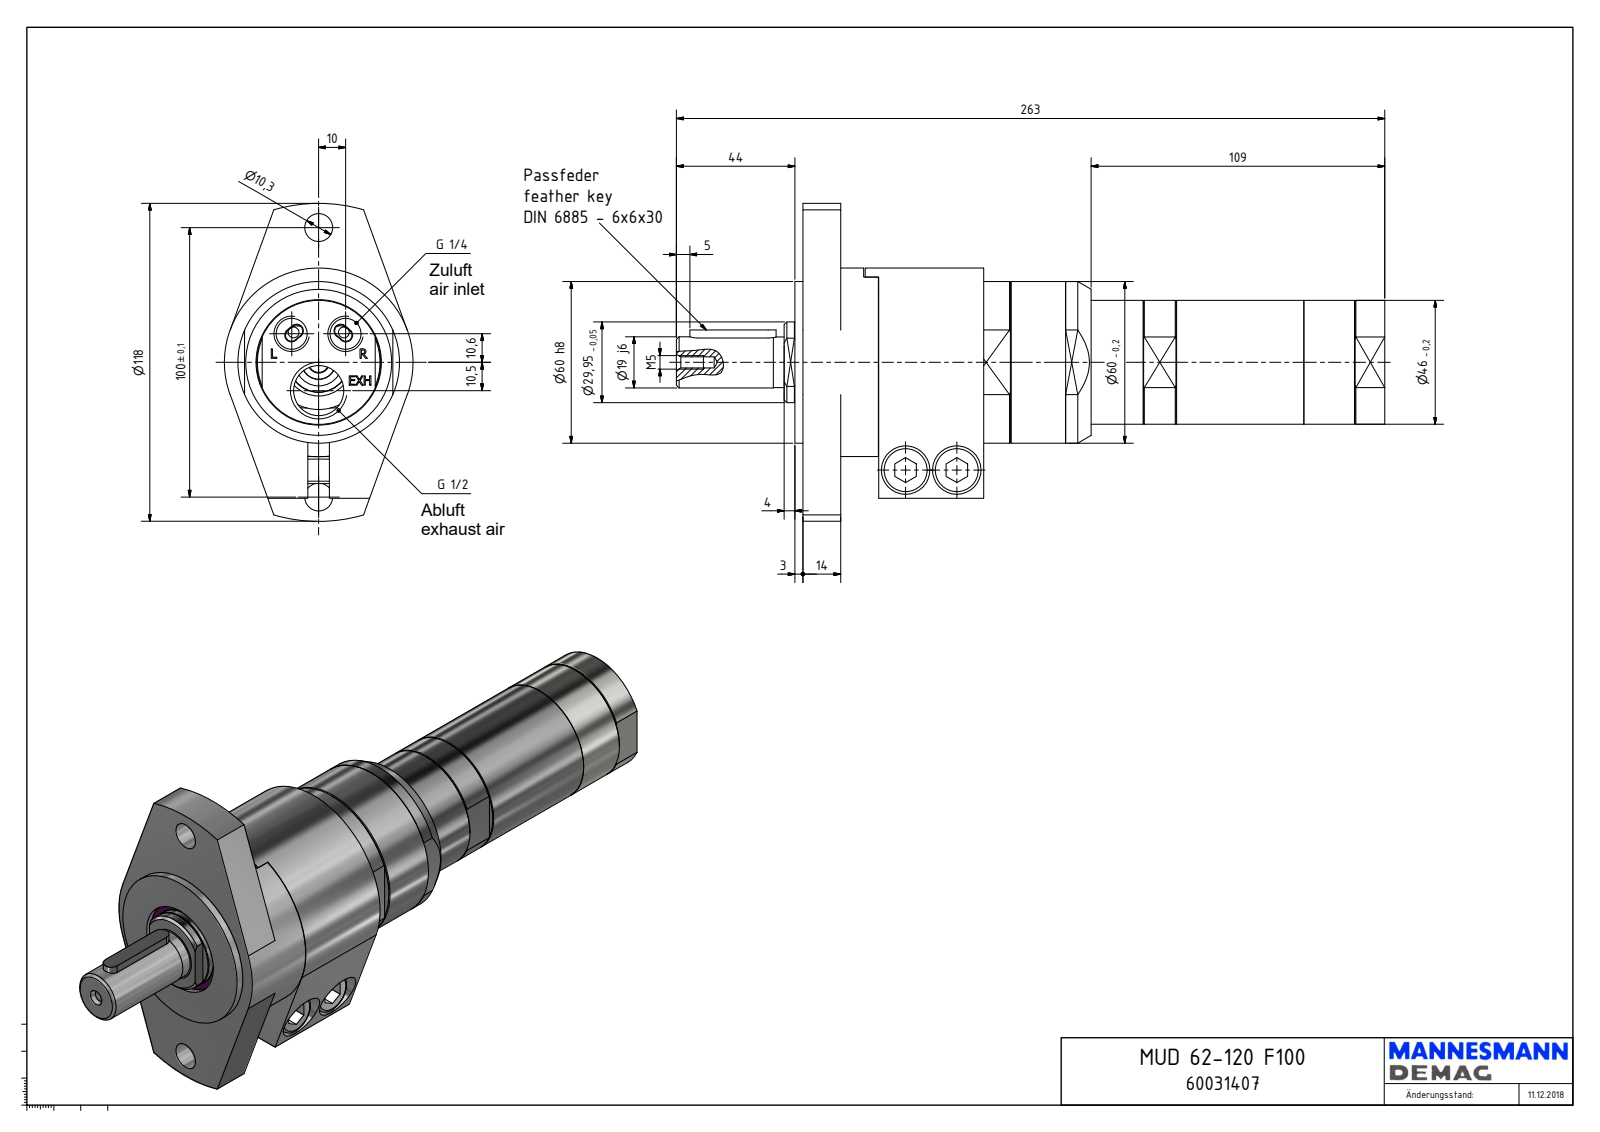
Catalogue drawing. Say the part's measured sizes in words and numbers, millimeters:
The part is named "MUD 62-120 F100_60031407". Its 3-D file was written by "Autodesk Inventor 2018 (AUTOMOTIVE_DESIGN)". It is 1 solid with 281 faces: 158 planar, 66 cylindrical and 57 other. Overall it measures 263 by 118 by 70 millimeters. Its volume is 619 354 cubic millimeters and its surface area 75 892 square millimeters. Round holes: 2 of diameter 8.38, 2 of diameter 10.3, 2 of diameter 10.5, 2 of diameter 11.45, 2 of diameter 18, 1 of diameter 1.55, 1 of diameter 4, 1 of diameter 4.13, 1 of diameter 5.5, 1 of diameter 18.63, 1 of diameter 35, 1 of diameter 36.5. Round bosses or shafts: 2 of diameter 16, 2 of diameter 10, 1 of diameter 70, 1 of diameter 60, 1 of diameter 55.18, 1 of diameter 46, 1 of diameter 41.66, 1 of diameter 33.52. Partial cylindrical surfaces (rounded edges, fillets, slot ends): 2 of radius 3, 2 of radius 5, 1 of radius 19, 1 of radius 25.44, 1 of radius 59. The main face-to-face distances are 14, 17, 3, 70.1, 67.1, 53.1, 31.1, 28.1, 14.1, 39. The hole center spacings are 14.57, 23.35, 40.65, 50, 61.42, 10.5, 19, 20.
